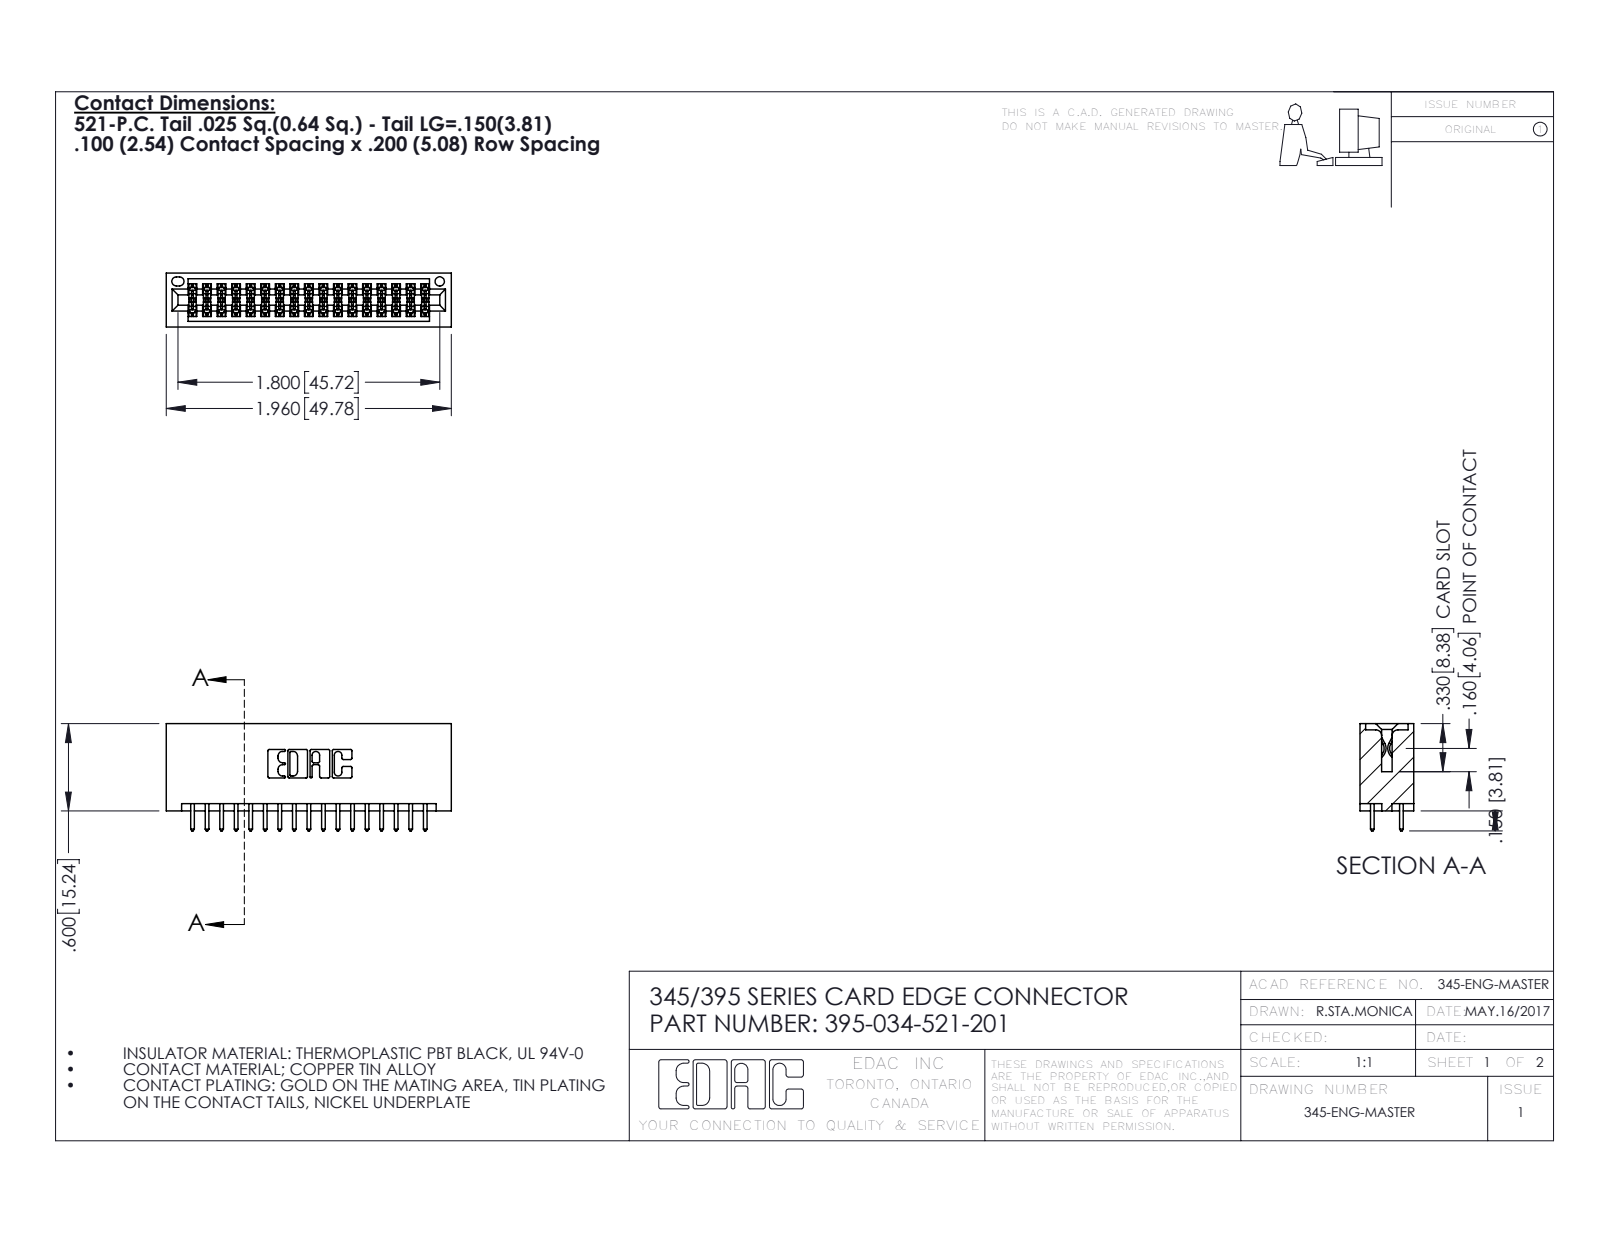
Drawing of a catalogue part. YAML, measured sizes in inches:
part_name: "395-034-521-201; 345 Part_No Mounting Lugs; 345-292-001_345-293-121"
step_written_by: "SolidWorks 2016 (CONFIG_CONTROL_DESIGN)"
units: inches
bodies: {solids: 35, faces: 1818, planar: 1198, cylindrical: 620, other: 0}
overall_size: [1.96, 0.737, 0.37]
volume: 0.318
surface_area: 11.51
round_holes:
  - {diameter: 0.064, count: 1}
partial_cylinders:
  - {radius: 0.006, count: 51}
  - {radius: 0.01, count: 34}
  - {radius: 0.01, count: 22}
  - {radius: 0.007, count: 6}
  - {radius: 0.031, count: 6}
  - {radius: 0.026, count: 3}
  - {radius: 0.014, count: 2}
  - {radius: 0.019, count: 2}
face_to_face_distances: [0.298, 0.072, 0.2, 0.37, 0.098, 0.272, 0.025, 0.225, 0.1, 0.175]
